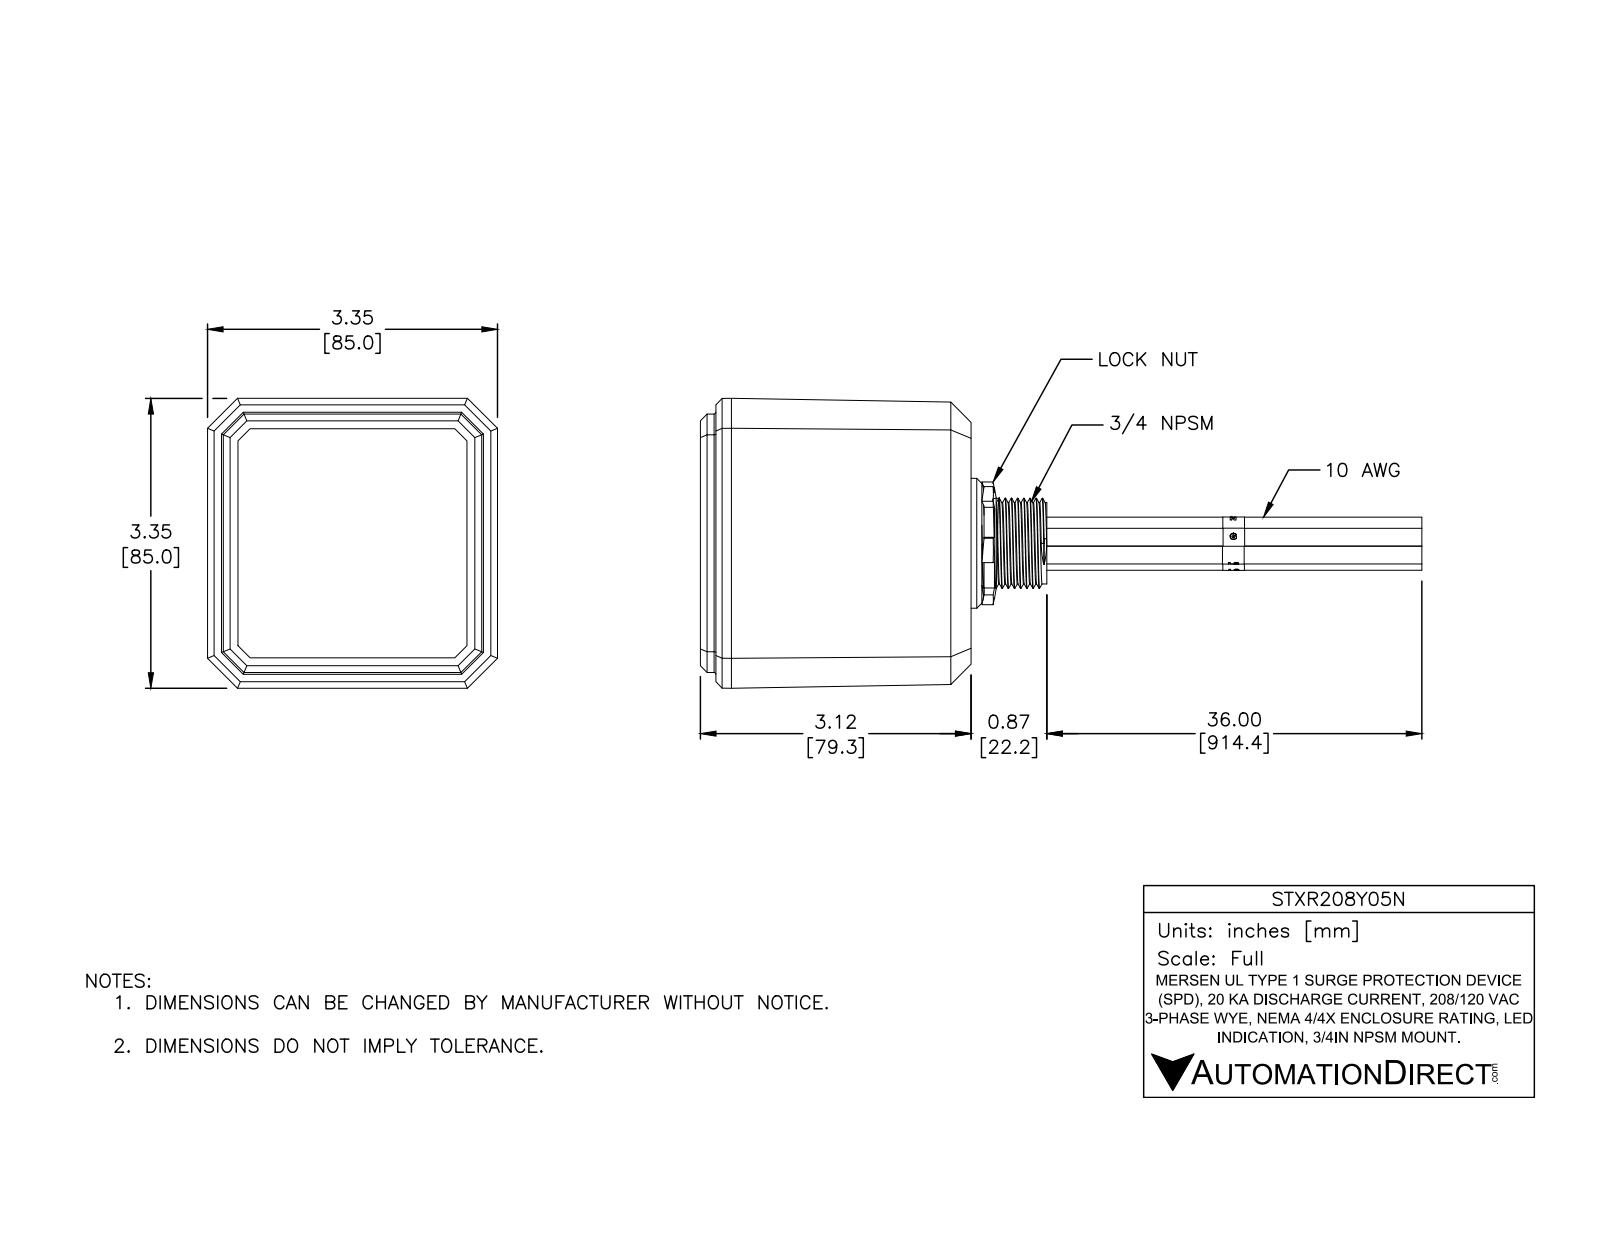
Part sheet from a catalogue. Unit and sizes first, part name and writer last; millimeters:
Units: millimetres
Overall size (bounding box): 211.5 × 85 × 85
Round holes (diameter × count): ⌀25.4 ×1
Round bosses / shafts (diameter × count): ⌀5.2 ×15, ⌀5.2 ×3, ⌀3.7 ×3, ⌀3.7 ×2, ⌀38.1 ×1, ⌀23.9 ×1
Partial cylindrical surfaces — rounded edges, fillets, slot ends (radius × count): R0.4 ×16, R0.5 ×8, R2.5 ×8, R1 ×4, R7.9 ×1, R16.2 ×1
Main face-to-face distances: 3.2, 3.2, 3, 75.9, 79, 72.7, 75.8, 70.3, 67.1, 5.7
Volume: 138 500 mm³ · Surface area: 96 000 mm²
Bodies: 8 solids, 525 faces (318 planar, 123 cylindrical, 84 other)
Part name (STEP PRODUCT): STXR208Y05N
STEP written by: SolidWorks 2016 (AUTOMOTIVE_DESIGN)
